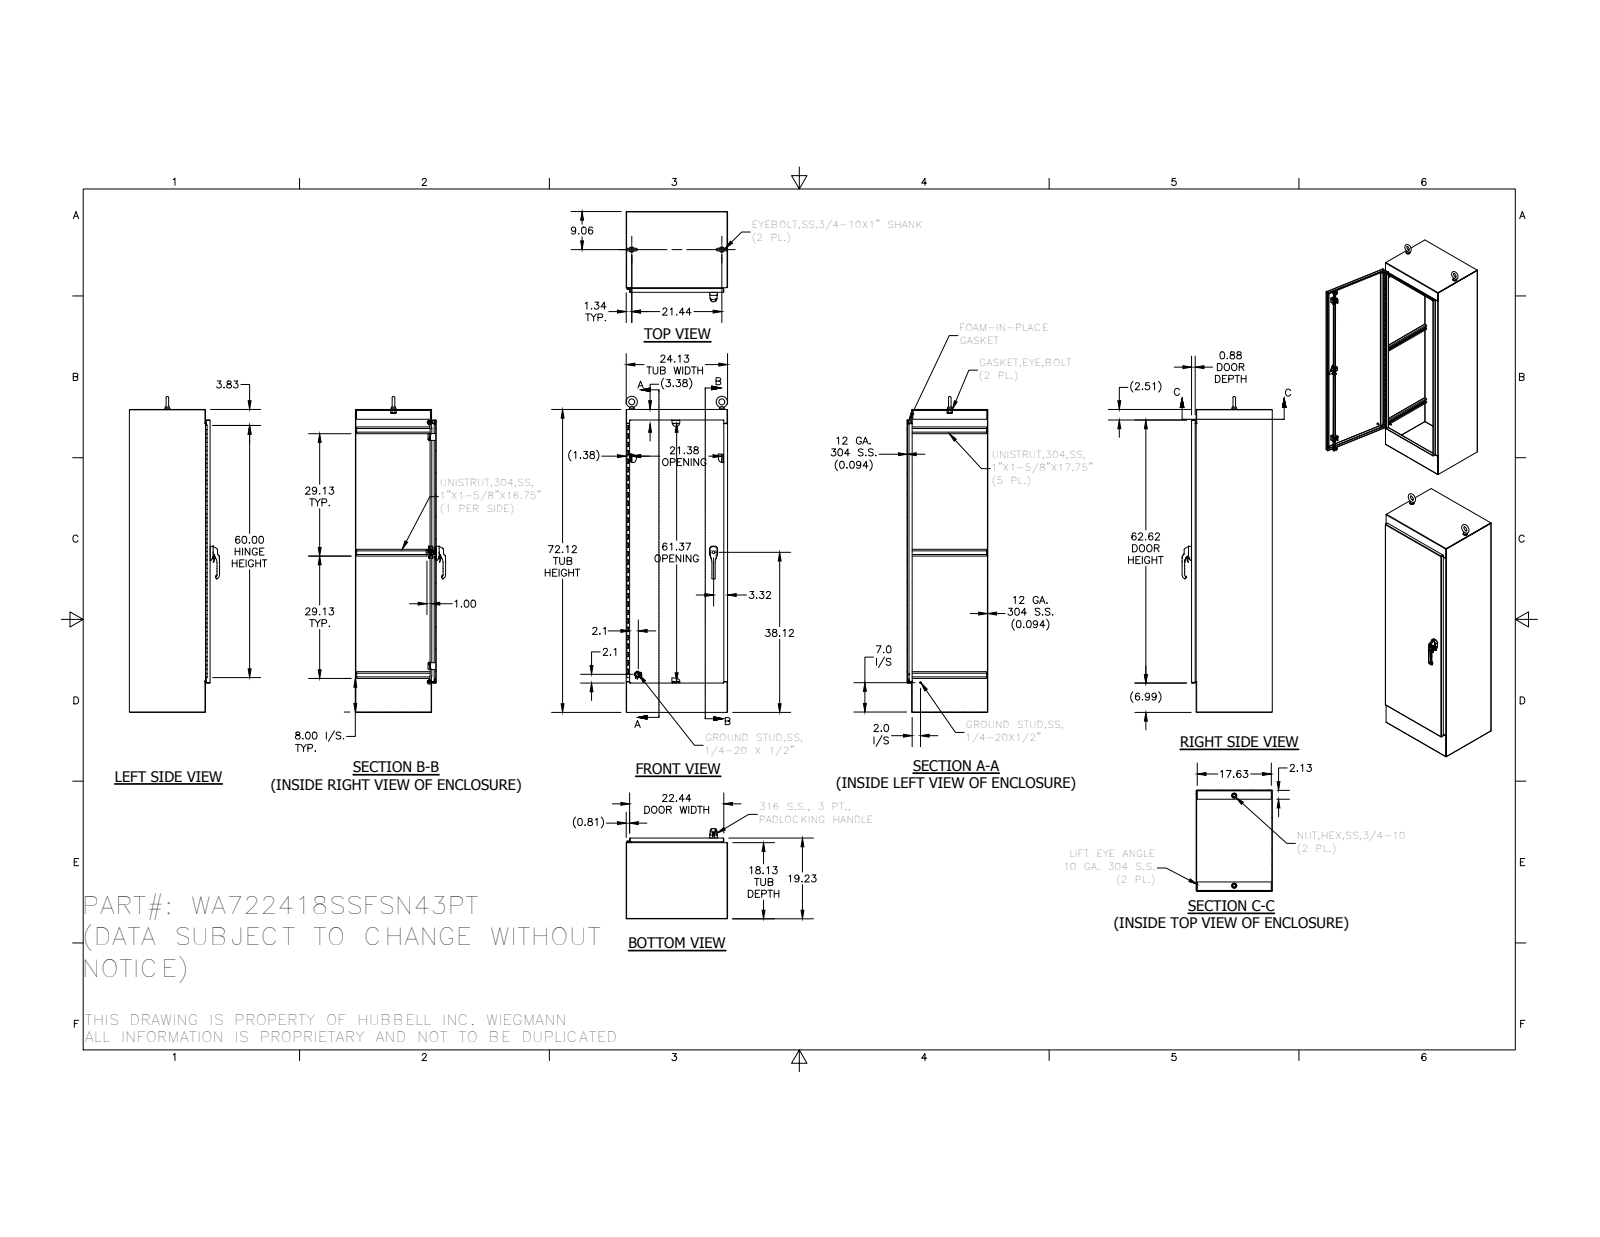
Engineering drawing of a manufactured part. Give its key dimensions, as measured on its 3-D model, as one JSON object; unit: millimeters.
{"part_name": "37029; HFW31712; 1091-903_AF0_2; 1091-B11_ASM (+8 more)", "step_written_by": "SolidWorks 2014 (AUTOMOTIVE_DESIGN)", "units": "millimeters", "bodies": {"solids": 64, "faces": 3471, "planar": 1220, "cylindrical": 1311, "other": 940}, "overall_size": [1911.3, 612.8, 545.5], "volume_mm3": 13460000, "surface_area_mm2": 10920000, "round_holes": [[6.7, 8], [9.5, 8], [4.7, 4], [5.4, 3], [6.4, 3], [7.1, 3], [6.1, 2], [6.4, 2], [8, 2], [10.2, 2], [10.2, 2], [10.5, 2]], "round_bosses_or_shafts": [[25.4, 3], [6, 3], [31.8, 2], [28.4, 2], [19.1, 2], [14.3, 2], [13.5, 2], [13.5, 2]], "partial_cylinders_radius": [[0.5, 172], [0.3, 106], [3.2, 26], [0.5, 21], [0.8, 19], [1.3, 19], [3.2, 15], [2, 14]], "face_to_face_distances": [2.4, 486, 610.4, 483.6, 608, 488.4, 612.8, 1829.6, 458, 28], "hole_center_spacings": [169.3, 508, 9.7, 19.3, 338.7, 677.3, 9.7, 12.5]}
